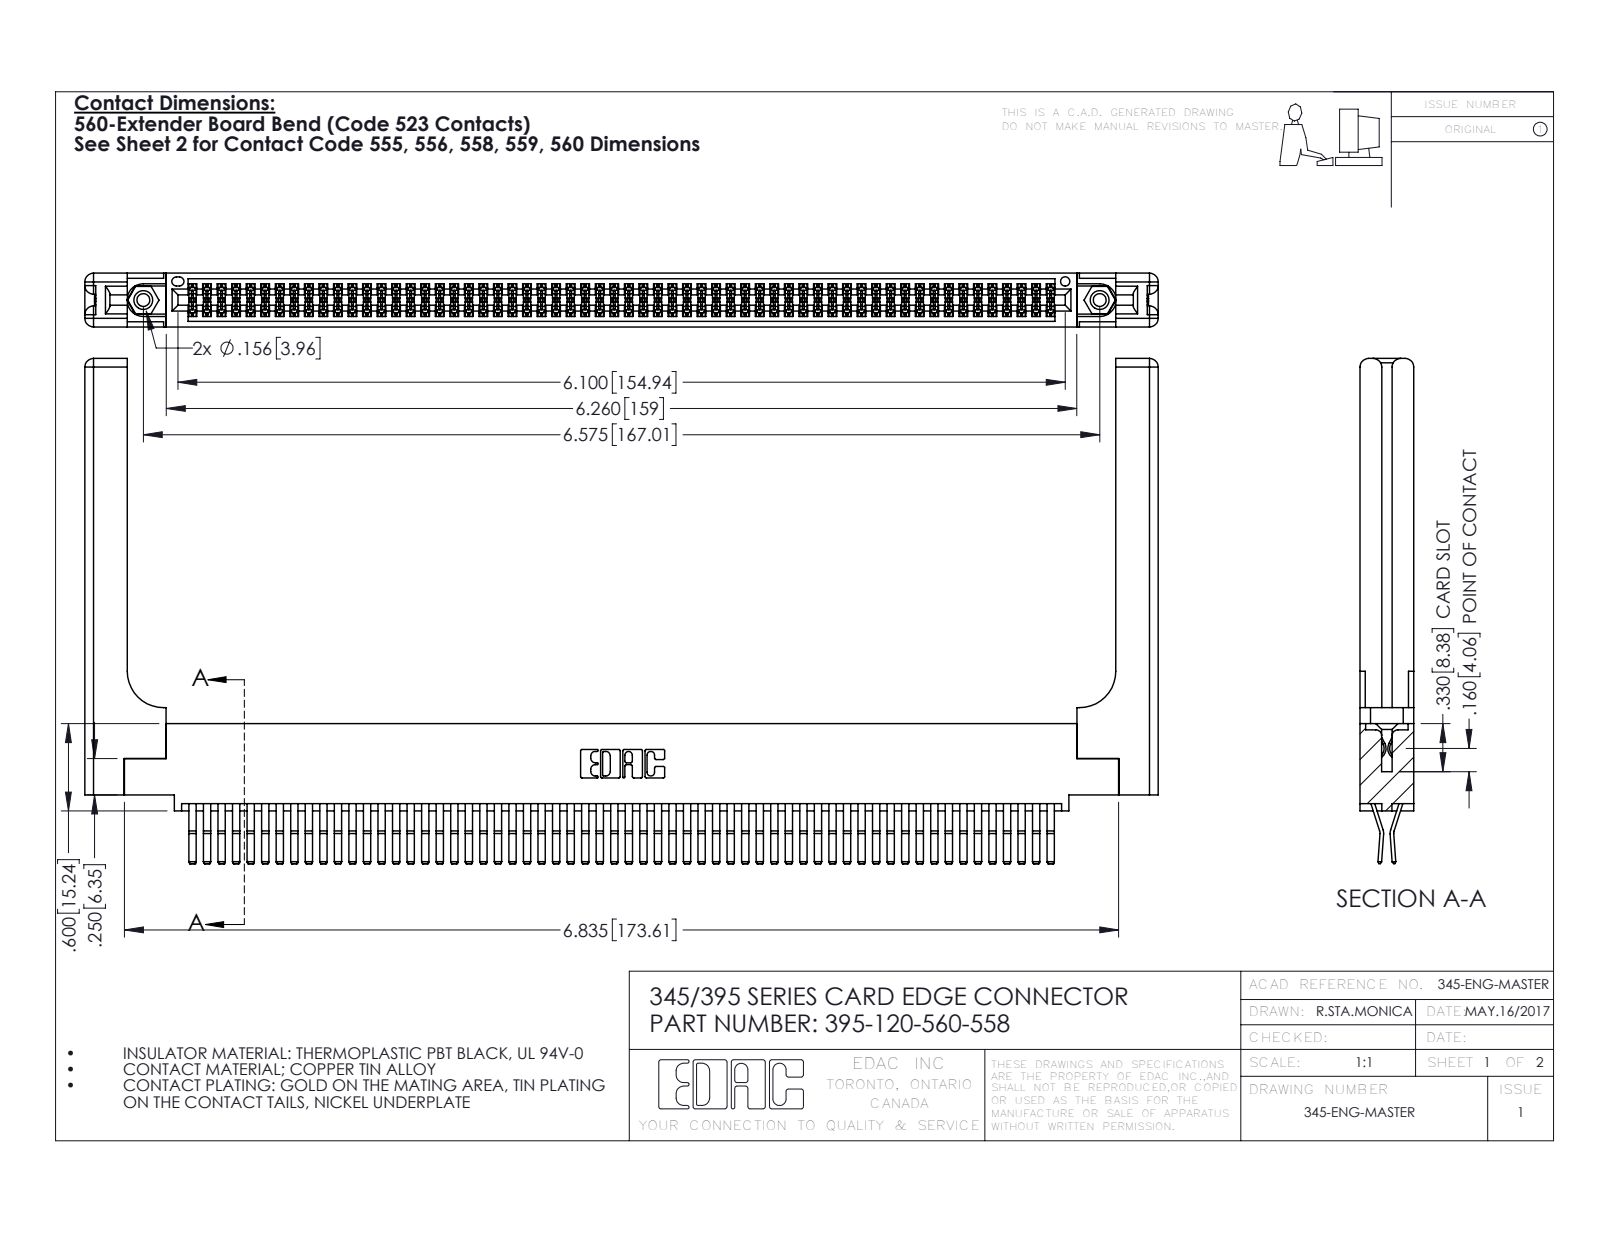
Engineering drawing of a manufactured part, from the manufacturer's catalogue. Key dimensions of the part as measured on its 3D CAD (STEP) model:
Part name (STEP PRODUCT): 345 Part_0.110 Offset - 0.156 Dia-TH; 395-120-560-558; 345-292-001_560 Tail; 345-220-058_345-220-058 (+1 more)
STEP written by: SolidWorks 2016 (CONFIG_CONTROL_DESIGN)
Units: inches
Bodies: 125 solids, 6626 faces (4192 planar, 2374 cylindrical, 60 other)
Overall size (bounding box): 7.379 × 3.472 × 0.37
Volume: 1.682 in³ · Surface area: 55.39 in²
Round holes (diameter × count): ⌀0.089 ×2, ⌀0.125 ×2, ⌀0.156 ×2, ⌀0.064 ×1
Round bosses / shafts (diameter × count): ⌀0.155 ×2
Partial cylindrical surfaces — rounded edges, fillets, slot ends (radius × count): R0.006 ×181, R0.01 ×22, R0.06 ×16, R0.007 ×6, R0.031 ×6, R0.026 ×3, R0.01 ×2, R0.014 ×2
Main face-to-face distances: 0.072, 0.298, 0.025, 0.37, 0.098, 0.272, 0.2, 0.225, 0.148, 0.15
Hole centre spacings: 0.27, 6.339, 6.575
